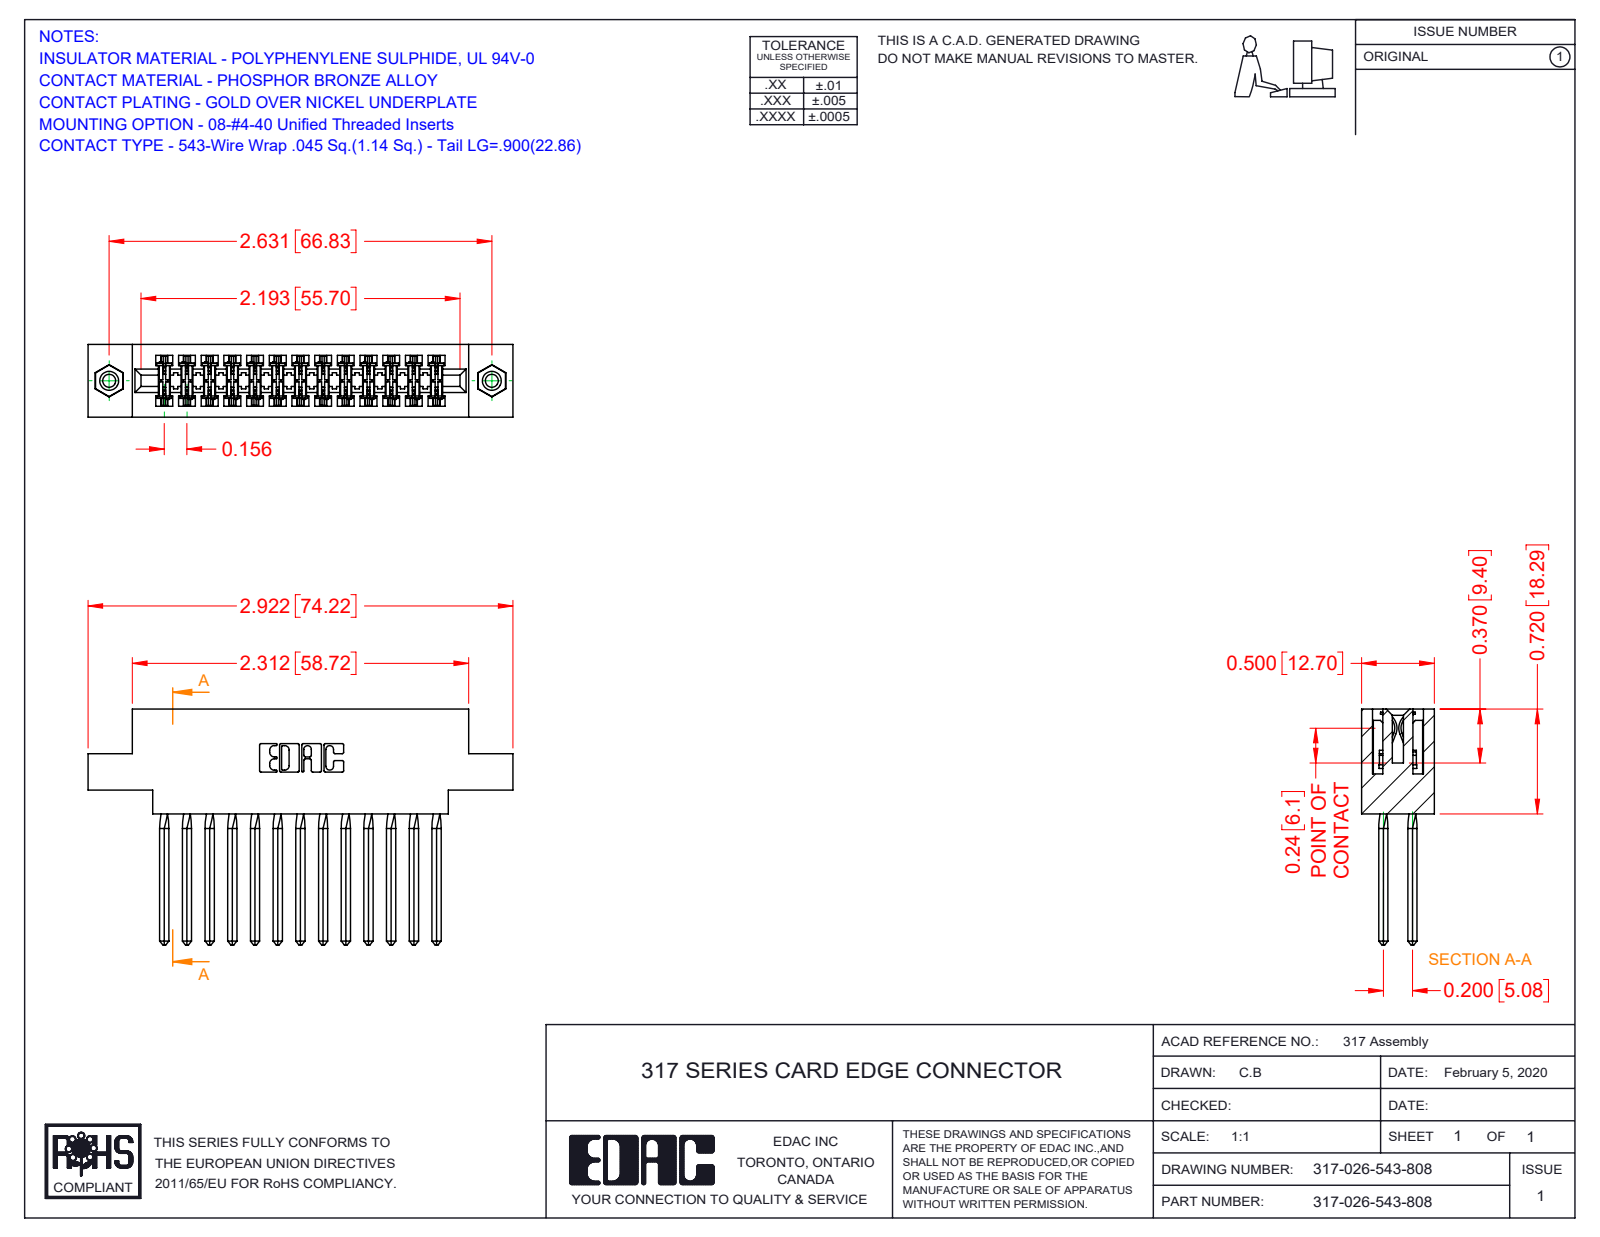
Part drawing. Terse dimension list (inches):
name: 317-290-001_543; 345-250-001_345-250-003-102; 317 Part_.156 Dia - TI; 317-026-543-878
written by: SolidWorks 2016 (CONFIG_CONTROL_DESIGN)
unit: in
bodies: 29 solids, 2476 faces (1988 planar, 368 cylindrical, 120 other)
size: 2.922 × 1.62 × 0.5
volume: 0.708 in³; area: 25.54 in²
holes: 2× ⌀0.089, 2× ⌀0.125, 2× ⌀0.156
bosses: 2× ⌀0.155
rounds: 52× R0.015, 22× R0.01, 6× R0.007, 6× R0.031, 3× R0.026, 2× R0.095, 2× R0.1, 2× R0.11
face distances: 0.5, 0.075, 0.425, 0.11, 0.22, 0.35, 0.331, 0.136, 0.72, 0.305
hole spacings: 2.631
